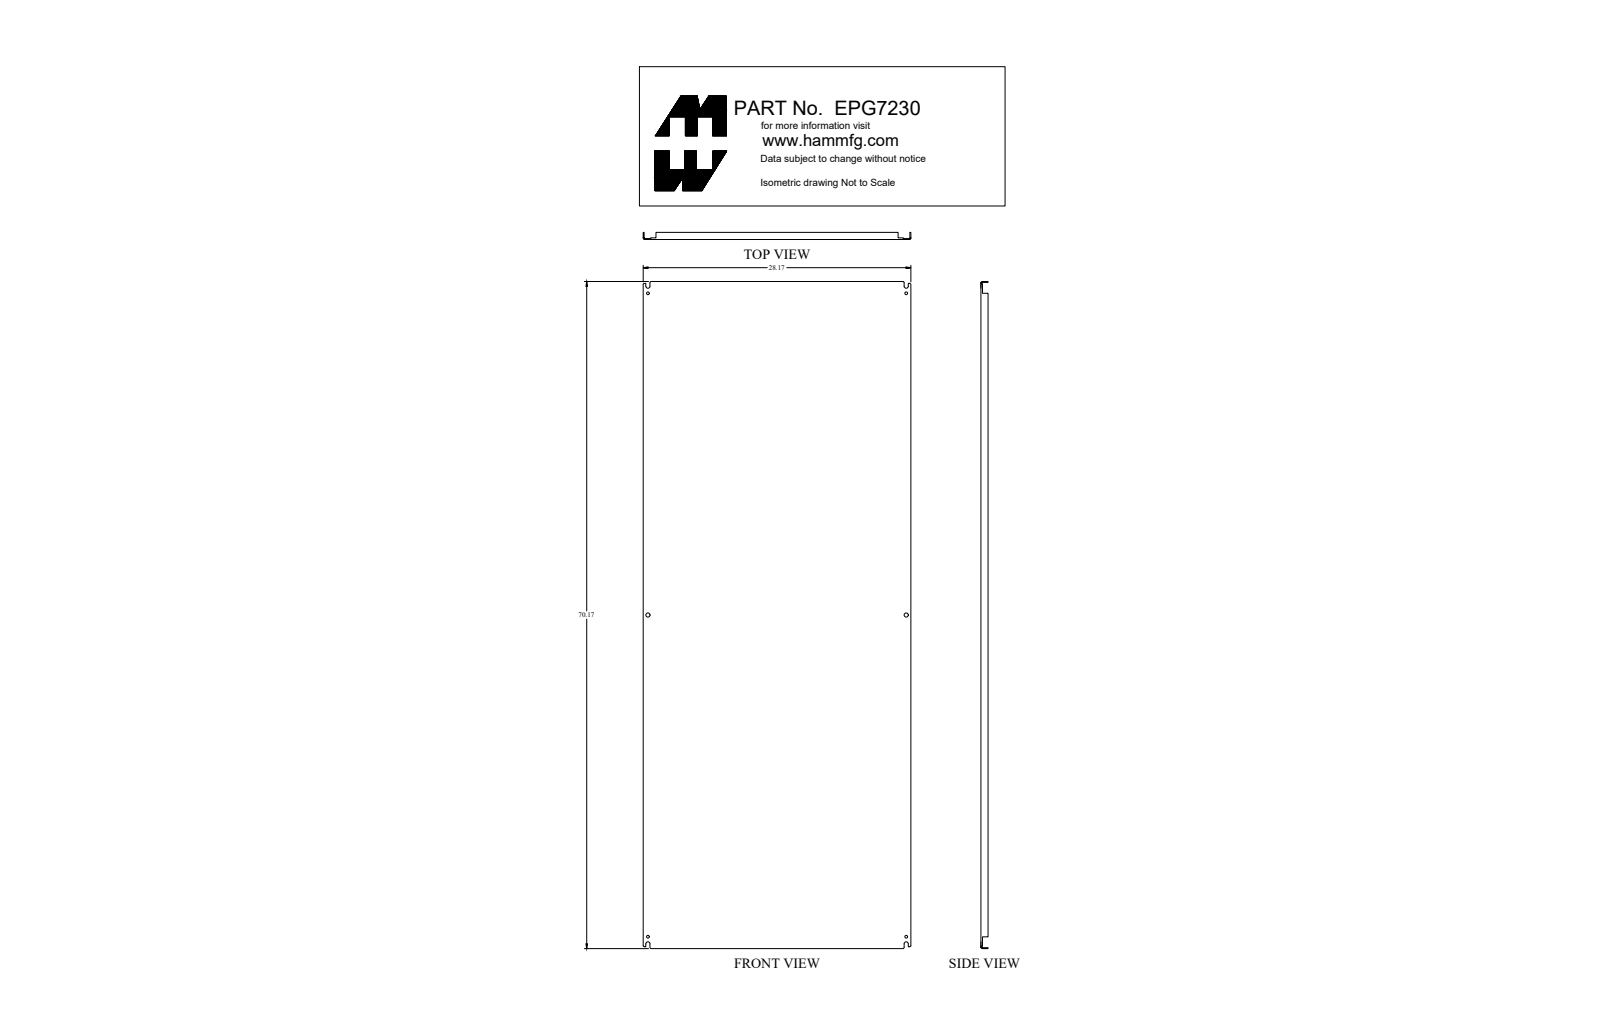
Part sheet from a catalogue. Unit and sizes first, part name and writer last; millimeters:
Units: millimetres
Overall size (bounding box): 1782.3 × 715.5 × 19.1
Round holes (diameter × count): ⌀7.1 ×4, ⌀11.1 ×2
Partial cylindrical surfaces — rounded edges, fillets, slot ends (radius × count): R1.2 ×4, R1.6 ×4, R3.6 ×4, R5.6 ×4
Main face-to-face distances: 2.4, 713.1, 715.5, 710.7, 1779.9, 19.1, 16.6, 1777.5, 1782.3, 4.3
Hole centre spacings: 859.6, 1102.7, 690.6, 1719.3, 1852.8
Volume: 3 253 000 mm³ · Surface area: 2 708 000 mm²
Bodies: 1 solid, 132 faces (74 planar, 42 cylindrical, 16 other)
Part name (STEP PRODUCT): EPG7230
STEP written by: SolidWorks 2018 (AUTOMOTIVE_DESIGN)
